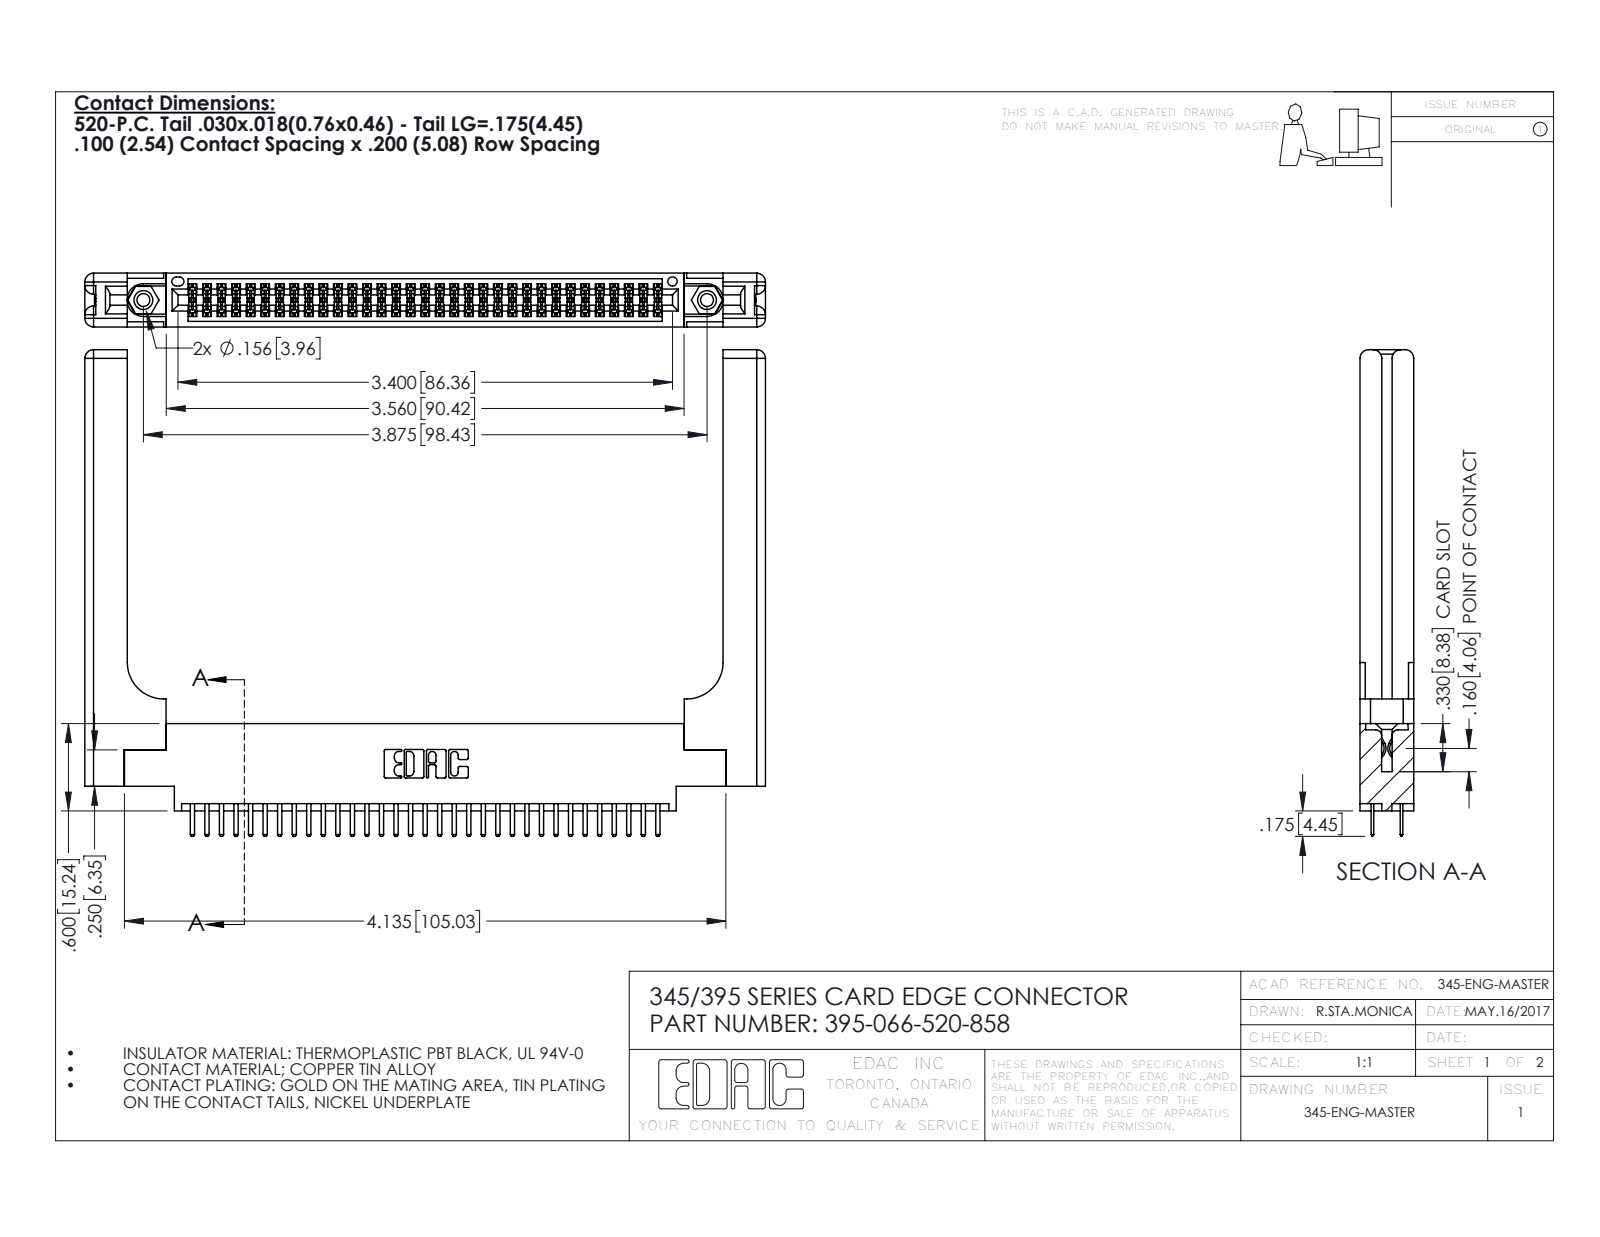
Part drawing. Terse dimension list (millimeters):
name: 395-066-520-858; 345 Part_0.170 Offset - 0.156 Dia-TH; 345-220-058_345-220-058; 345-250-001_345-250-001-102 (+1 more)
written by: SolidWorks 2016 (CONFIG_CONTROL_DESIGN)
unit: mm
bodies: 71 solids, 3950 faces (2542 planar, 1348 cylindrical, 60 other)
size: 118.8 × 85 × 9.4
volume: 19 800 mm³; area: 21 700 mm²
holes: 2× ⌀2.3, 2× ⌀3.2, 2× ⌀4, 1× ⌀1.6
bosses: 2× ⌀3.9
rounds: 99× R0.2, 70× R0.3, 22× R0.3, 16× R1.5, 6× R0.2, 6× R0.8, 3× R0.7, 2× R0.4
face distances: 9.4, 1.8, 7.6, 5.1, 2.5, 6.9, 0.6, 5.7, 3.8, 3.8
hole spacings: 6.9, 92.5, 98.4
